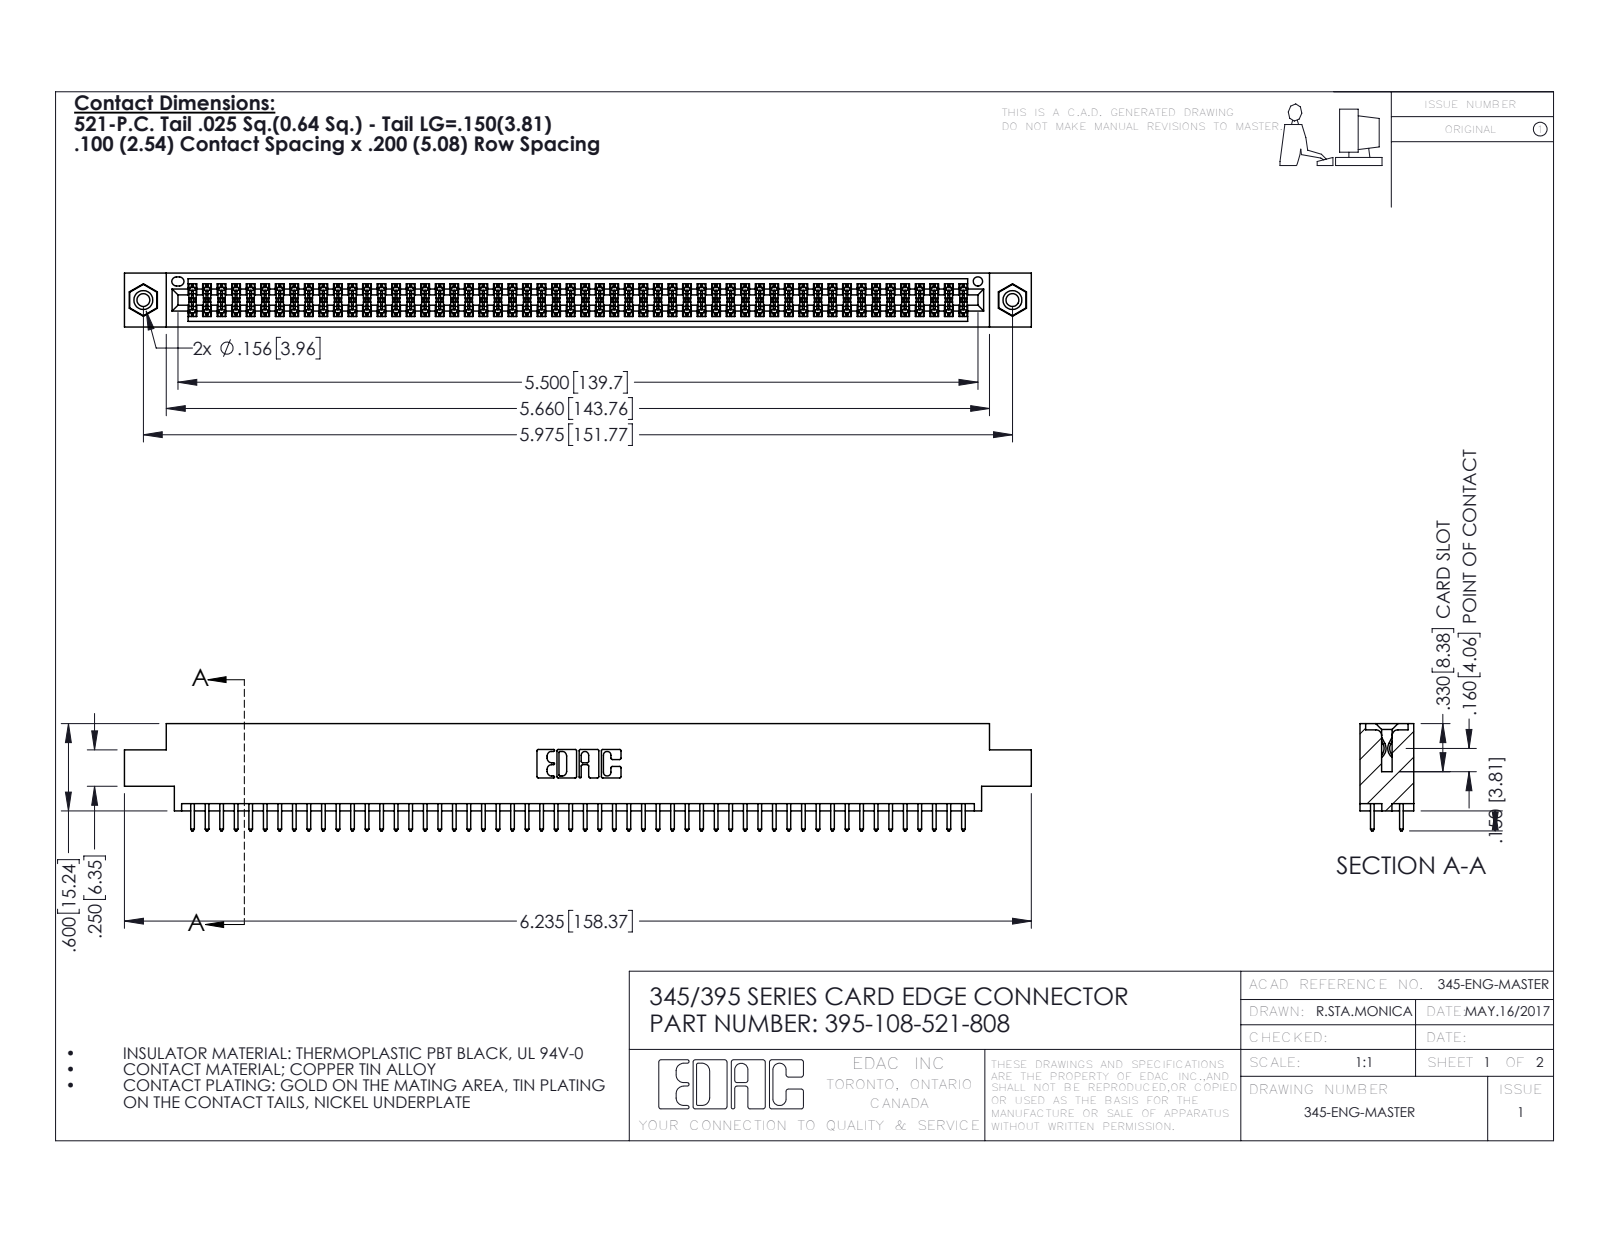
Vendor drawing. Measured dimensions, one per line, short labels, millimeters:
name: 345-250-001_345-250-003-102; 345-292-001_345-293-121; 345 Part_0.170 Offset - 0.156 Dia-TI; 395-108-521-808
written by: SolidWorks 2016 (CONFIG_CONTROL_DESIGN)
unit: mm
bodies: 111 solids, 5590 faces (3680 planar, 1894 cylindrical, 16 other)
size: 158.4 × 18.7 × 9.4
volume: 15 300 mm³; area: 22 770 mm²
holes: 2× ⌀2.3, 2× ⌀3.2, 2× ⌀4, 1× ⌀1.6
bosses: 2× ⌀3.9
rounds: 162× R0.2, 108× R0.3, 22× R0.3, 6× R0.2, 6× R0.8, 3× R0.7, 2× R0.4, 2× R0.5
face distances: 1.8, 7.6, 5.1, 9.4, 2.5, 6.9, 0.6, 5.7, 4.4, 3.8
hole spacings: 6.9, 145.8, 151.8
